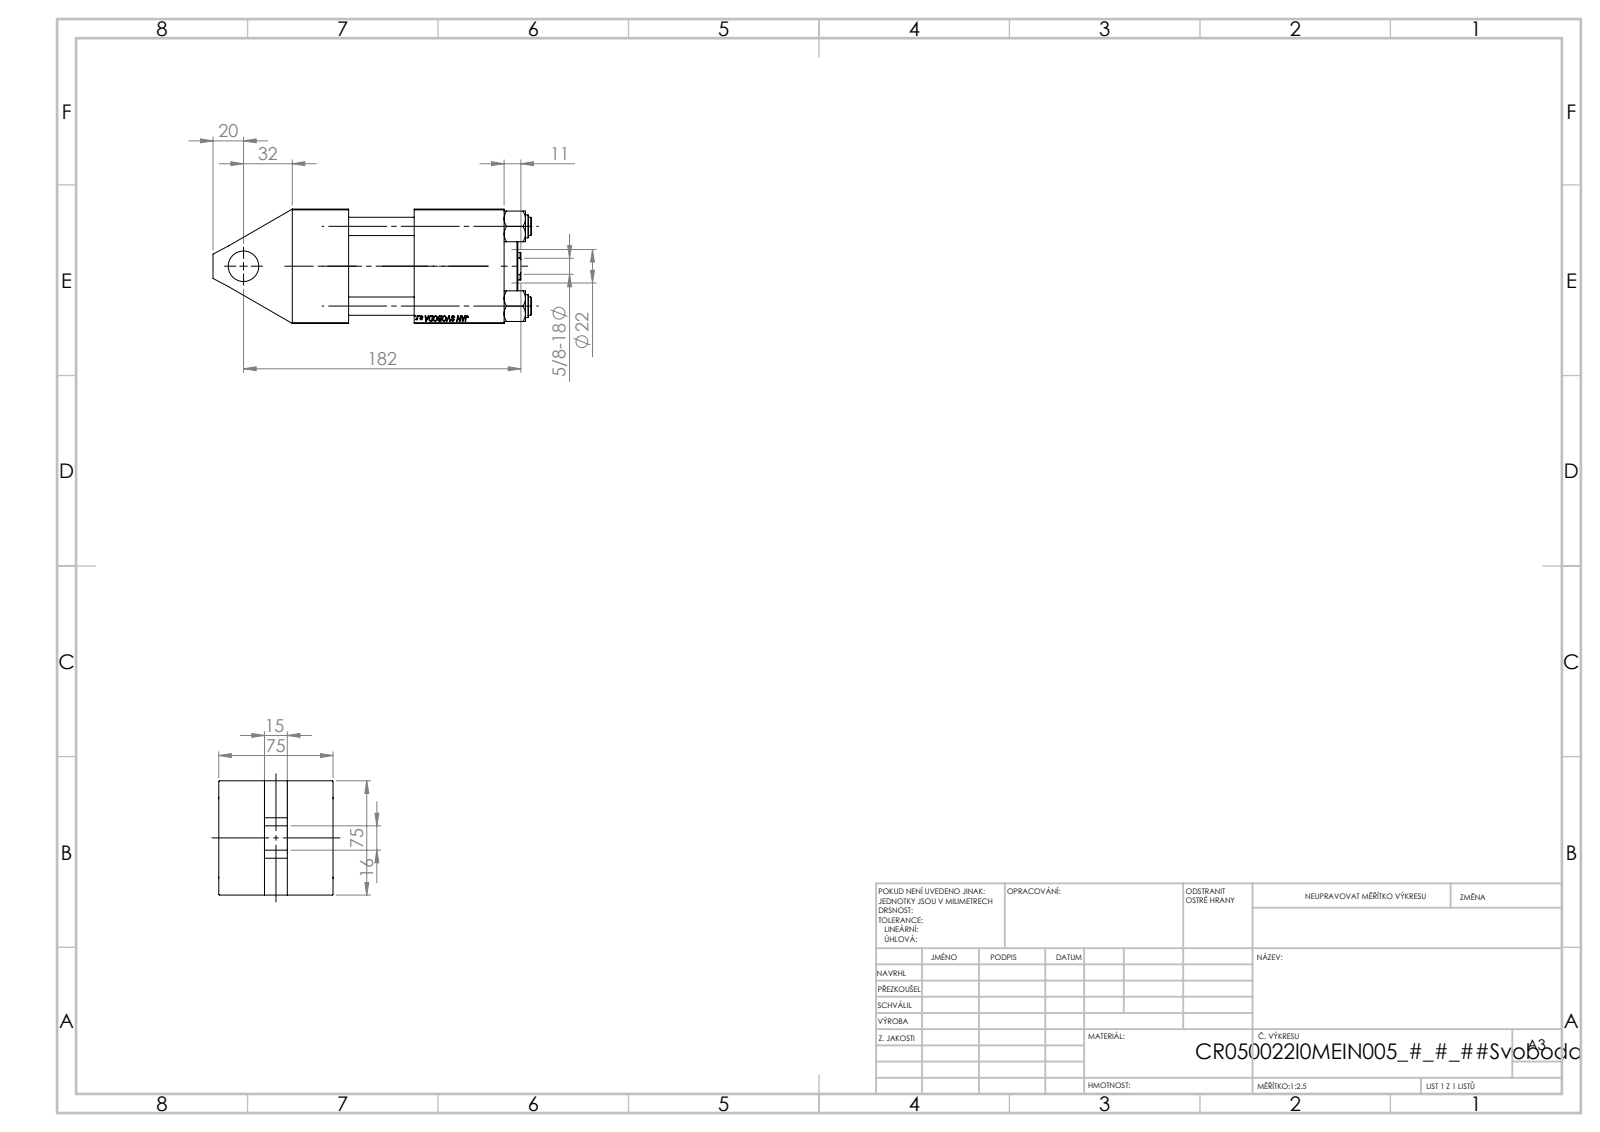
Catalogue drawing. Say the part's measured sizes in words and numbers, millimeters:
The part is named "NUT_M5_I; V215CR_I_Body; V215CR_TYCINKA_I; V215CR_VCP_I (+1 more)". Its 3-D file was written by "SolidWorks 2019 (CONFIG_CONTROL_DESIGN)". It is 11 solids with 1078 faces: 502 planar, 80 cylindrical and 496 other. Overall it measures 209 by 75.54 by 75 millimeters. Its volume is 657 318 cubic millimeters and its surface area 145 952 square millimeters. Round holes: 4 of diameter 12, 2 of diameter 7, 2 of diameter 20.96, 2 of diameter 30, 1 of diameter 10.5, 1 of diameter 20, 1 of diameter 22, 1 of diameter 25, 1 of diameter 41, 1 of diameter 50, 1 of diameter 53. Round bosses or shafts: 4 of diameter 15, 1 of diameter 56, 1 of diameter 34. Partial cylindrical surfaces (rounded edges, fillets, slot ends): 1 of radius 10.5. The main face-to-face distances are 75, 102, 37, 139, 45, 30, 43, 59, 80, 73.3. The hole center spacings are 36.98, 52.3, 73.96, 78.5.
